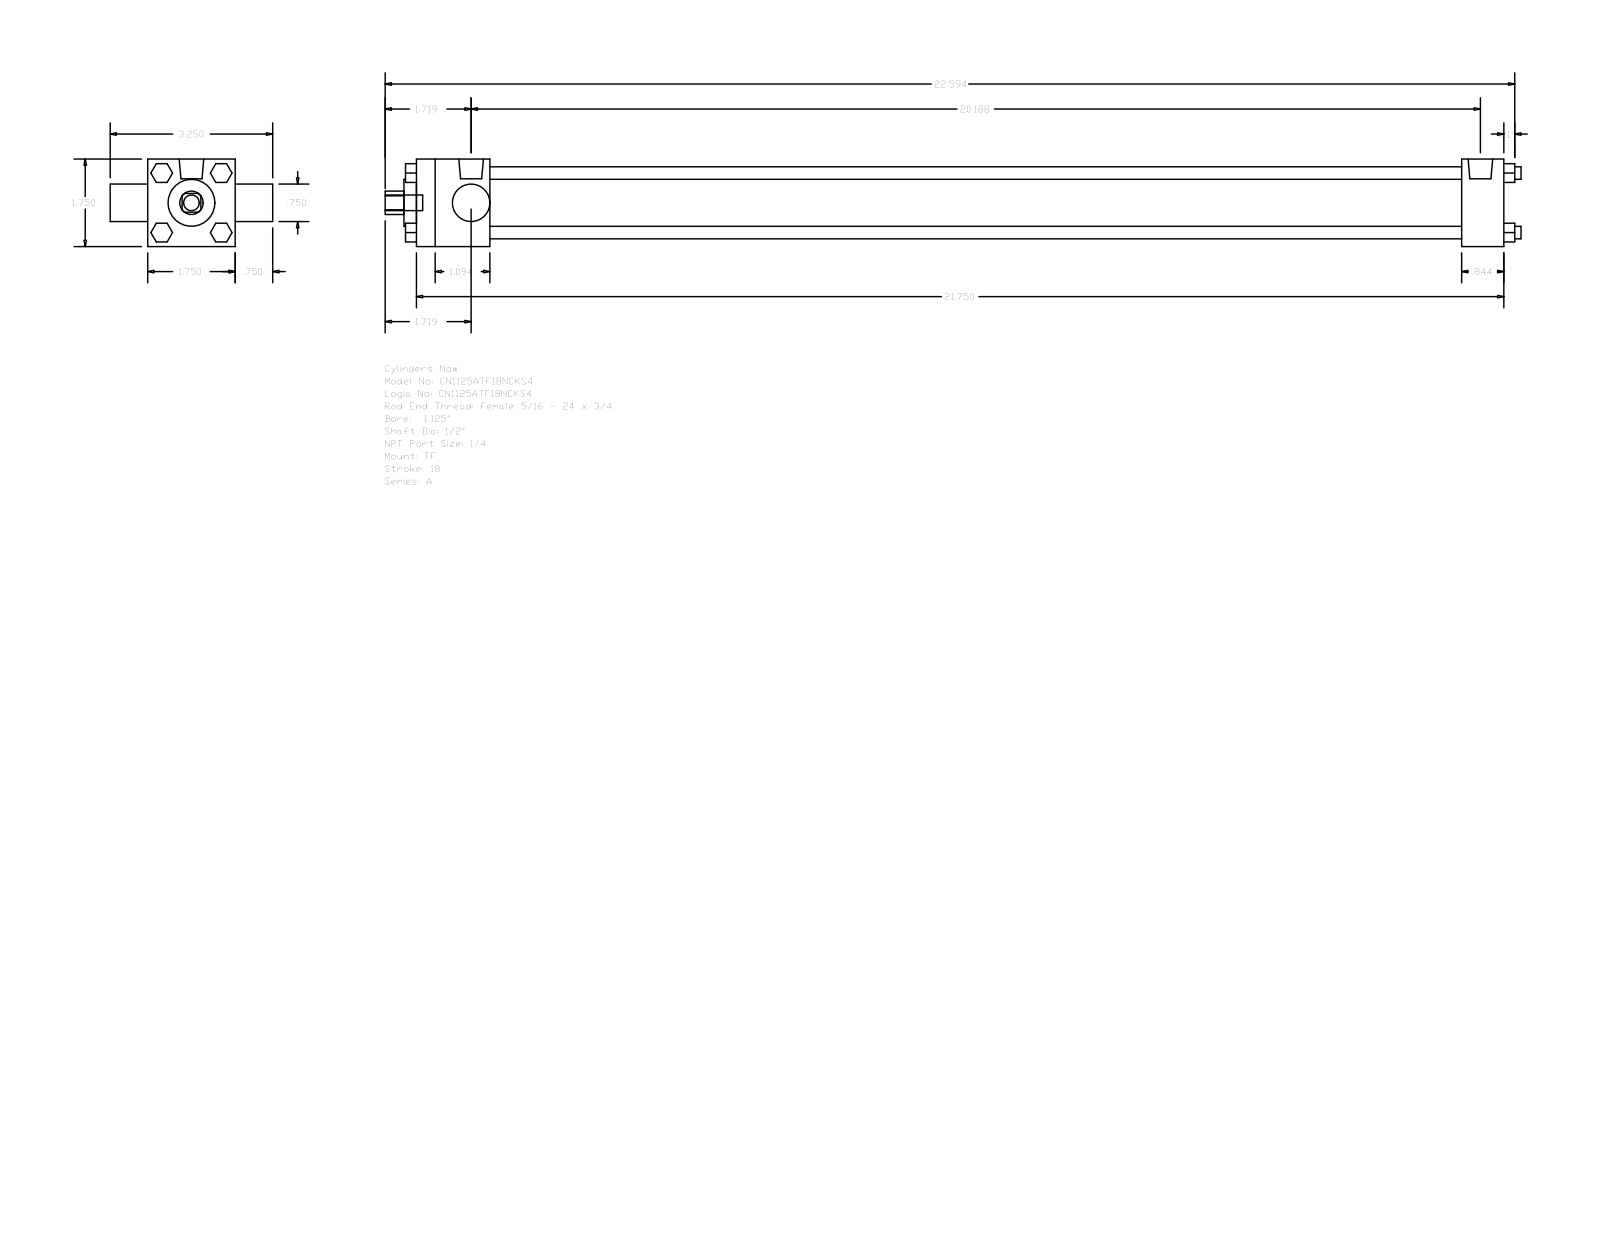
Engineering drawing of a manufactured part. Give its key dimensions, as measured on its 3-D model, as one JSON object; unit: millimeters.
{"part_name": "A_TF__0112_0.5", "step_written_by": "GSSL Pune (CONFIG_CONTROL_DESIGN)", "units": "millimeters", "bodies": {"solids": 0, "faces": 120, "planar": 92, "cylindrical": 28, "other": 0}, "overall_size": [577.06, 82.55, 44.45], "round_holes": [[12.7, 1], [19.05, 1], [23.81, 1], [31.88, 1]], "round_bosses_or_shafts": [[6.35, 4], [5.56, 3], [12.49, 2], [7.94, 1]], "partial_cylinders_radius": [[5.94, 1]], "face_to_face_distances": [44.46, 552.45, 531.01, 21.44, 37.3, 493.71, 515.15, 19.04, 63.5, 9.53]}
